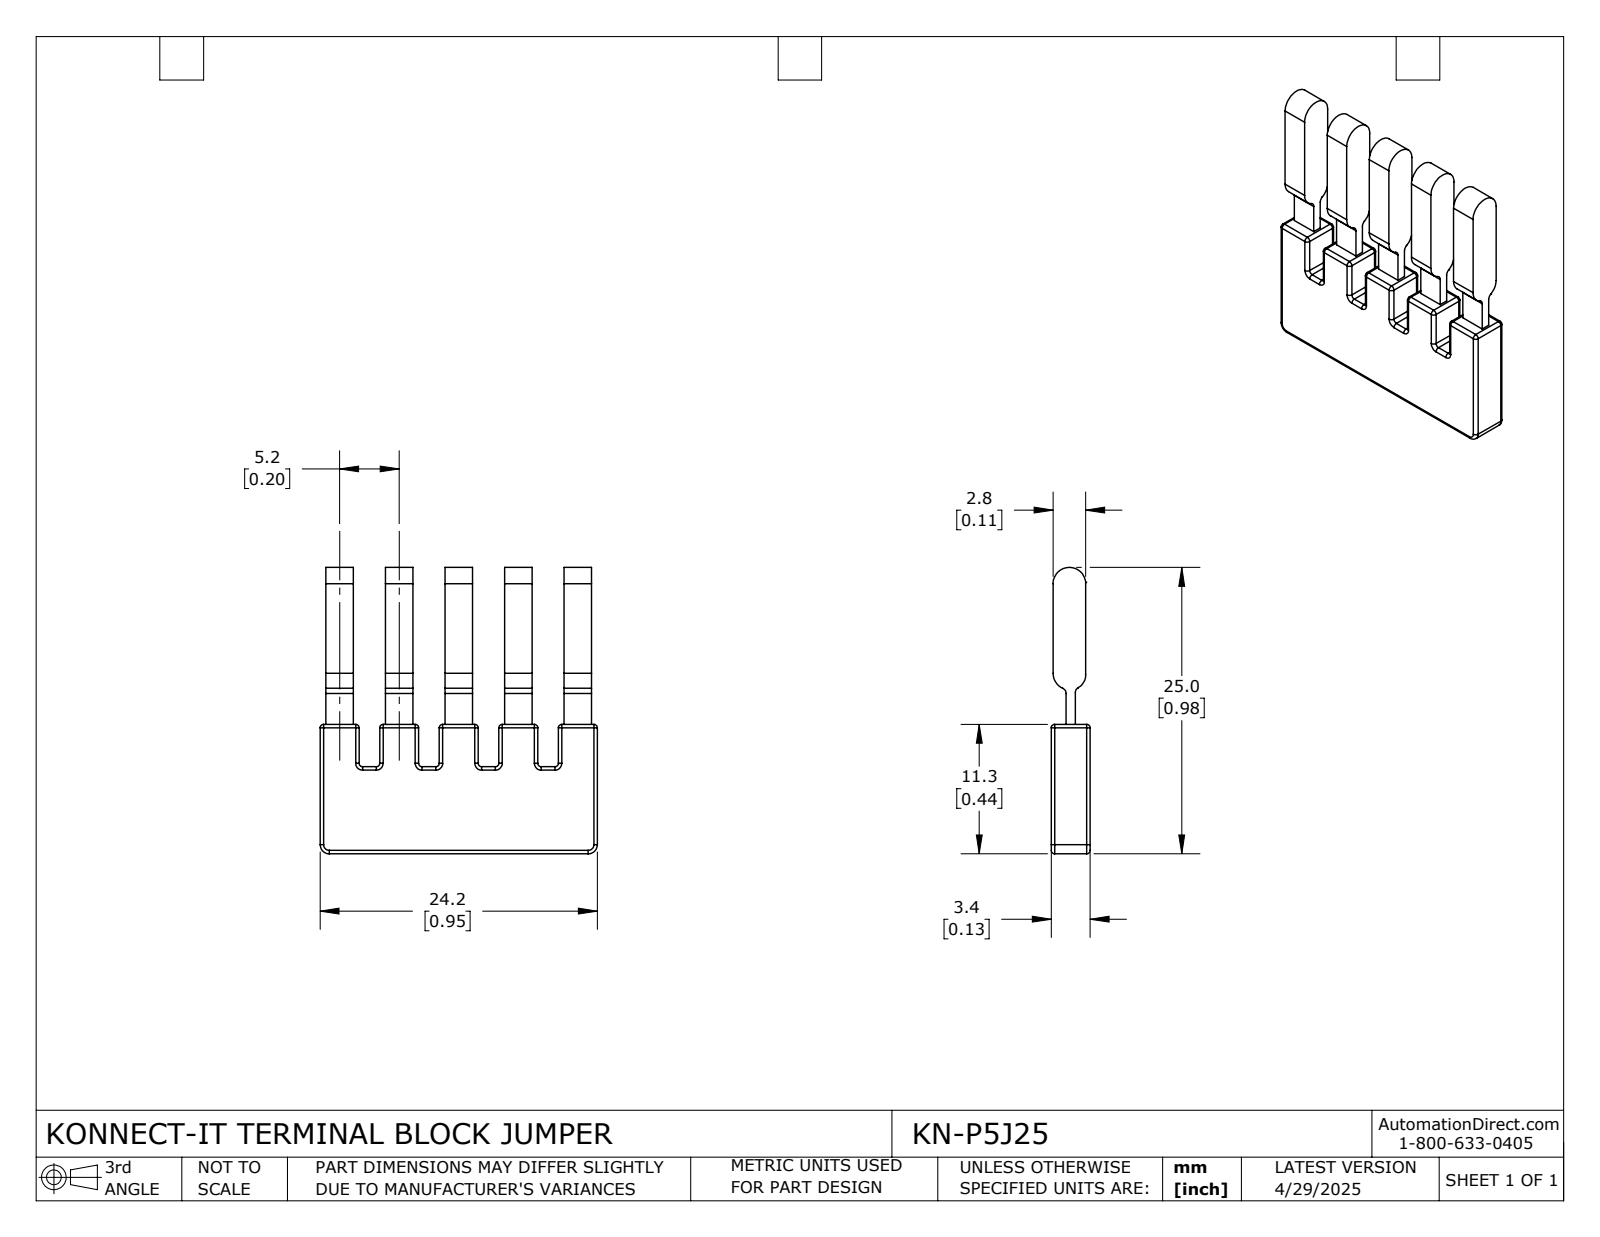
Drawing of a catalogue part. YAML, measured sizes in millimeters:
part_name: "KN-P5J25"
step_written_by: "SolidWorks 2024 (CONFIG_CONTROL_DESIGN)"
units: millimeters
bodies: {solids: 1, faces: 188, planar: 59, cylindrical: 89, other: 40}
overall_size: [25, 24.2, 3.4]
volume: 1209
surface_area: 1460
partial_cylinders:
  - {radius: 0.3, count: 44}
  - {radius: 0.5, count: 2}
  - {radius: 0.8, count: 2}
  - {radius: 1.43, count: 2}
  - {radius: 2, count: 2}
  - {radius: 1.3, count: 1}
face_to_face_distances: [5.2, 3.4, 10.4, 15.6, 2.4, 7.6, 0.5, 2.9, 2.8, 5.7]
